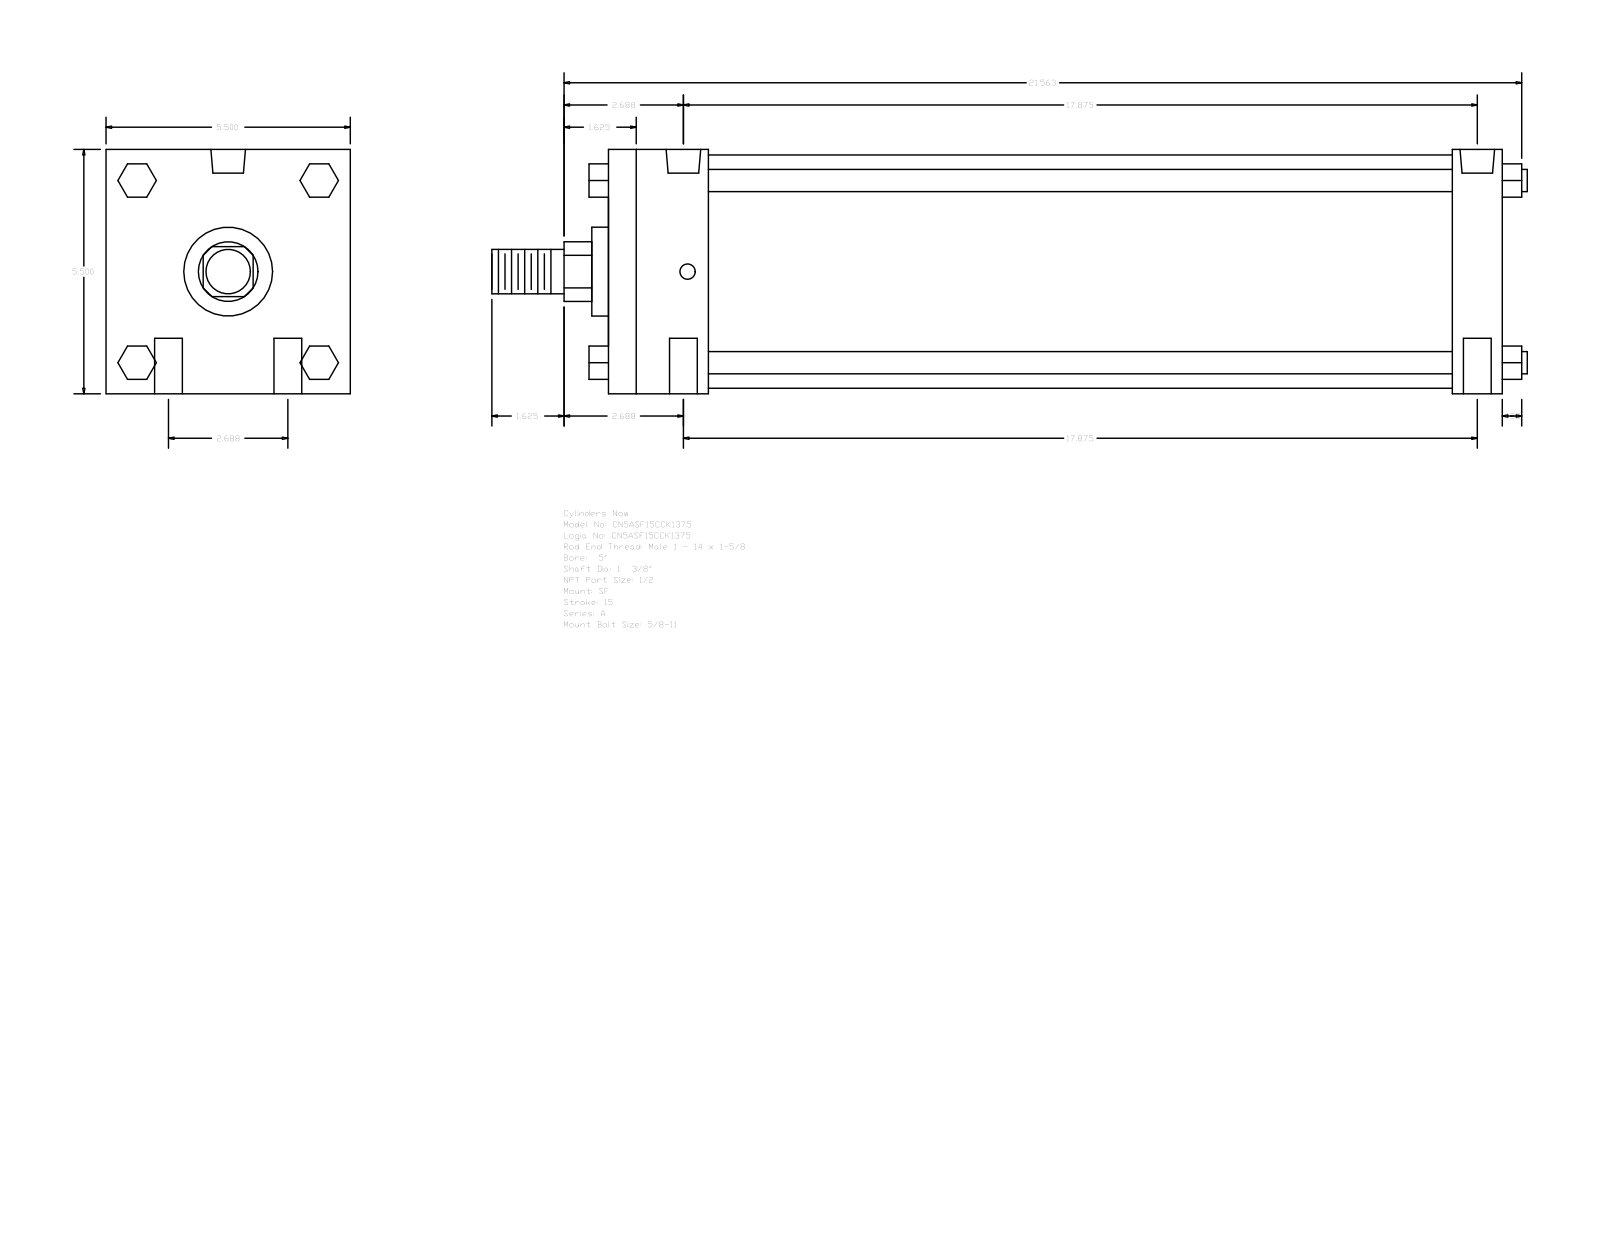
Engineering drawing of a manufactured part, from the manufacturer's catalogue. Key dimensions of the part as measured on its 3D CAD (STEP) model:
Part name (STEP PRODUCT): A_SF__0500_1.375
STEP written by: GSSL Pune (CONFIG_CONTROL_DESIGN)
Units: millimetres
Bodies: 0 solids, 124 faces (94 planar, 30 cylindrical, 0 other)
Overall size (bounding box): 592.14 × 139.7 × 139.7
Round holes (diameter × count): ⌀15.88 ×4, ⌀8.73 ×2, ⌀19.77 ×2
Round bosses / shafts (diameter × count): ⌀12.7 ×4, ⌀133.35 ×1, ⌀50.8 ×1, ⌀34.92 ×1, ⌀25.4 ×1
Partial cylindrical surfaces — rounded edges, fillets, slot ends (radius × count): R17.06 ×1
Main face-to-face distances: 139.7, 511.18, 57.15, 28.58, 482.6, 425.45, 454.03, 19.05, 52.07, 90.18
Hole centre spacings: 34.13, 455.31, 454.03, 68.26, 459.13, 449.25
